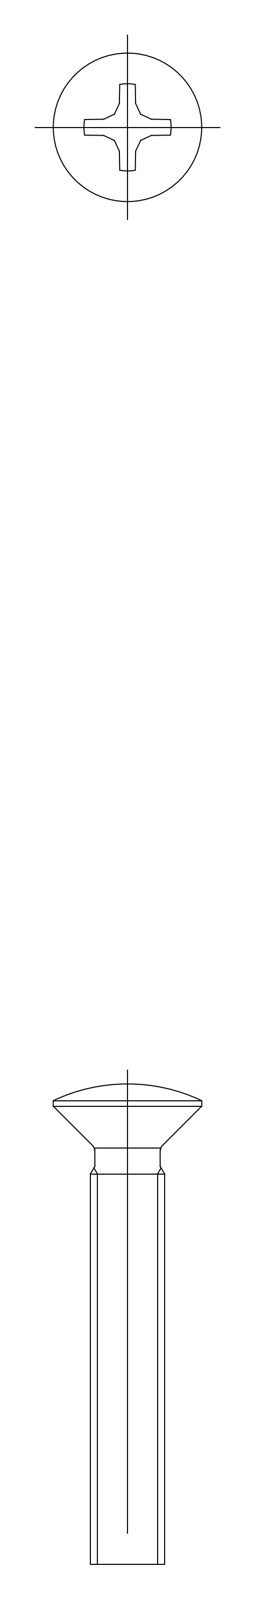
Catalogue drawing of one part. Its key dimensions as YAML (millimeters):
part_name: "screw"
step_written_by: "CADfix (AUTOMOTIVE_DESIGN)"
units: millimeters
bodies: {solids: 1, faces: 27, planar: 0, cylindrical: 0, other: 27}
overall_size: [25.88, 8, 8]
volume: 373
surface_area: 425
